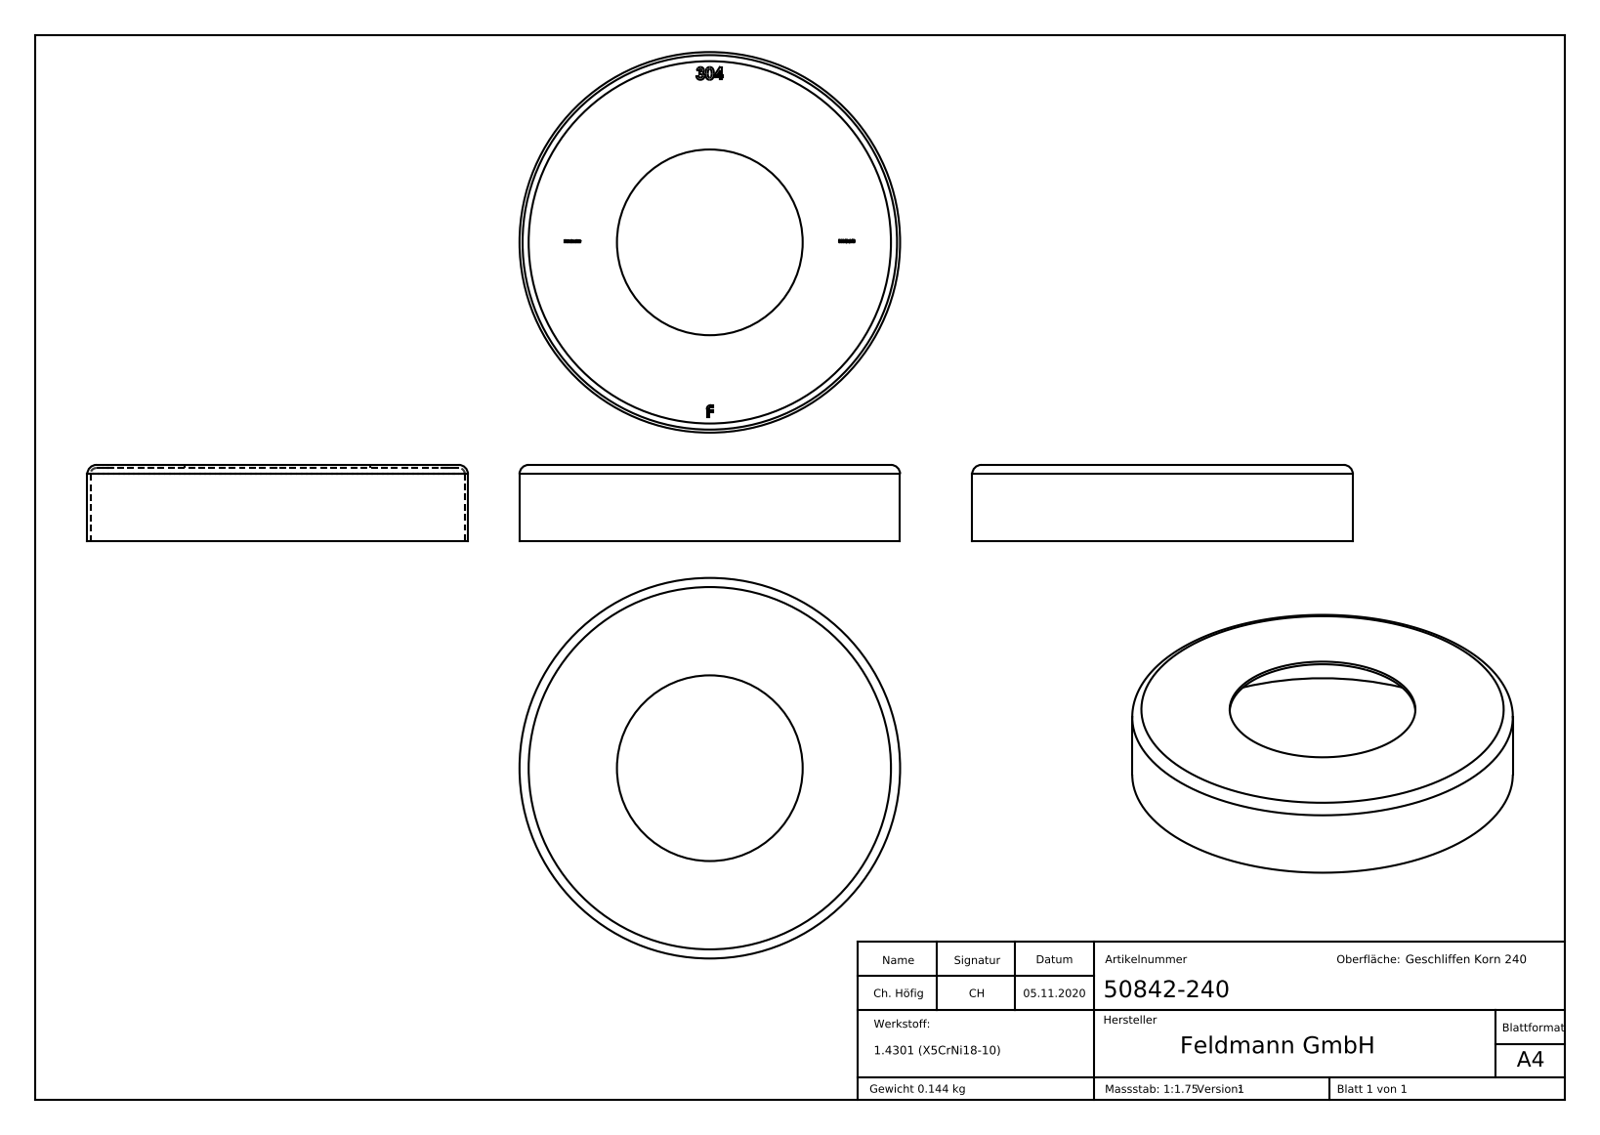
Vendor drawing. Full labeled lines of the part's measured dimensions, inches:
Part name (STEP PRODUCT): 50842-240
STEP written by: SolidWorks 2018 (CONFIG_CONTROL_DESIGN)
Units: inches
Bodies: 1 solid, 302 faces (164 planar, 6 cylindrical, 132 other)
Overall size (bounding box): 4.921 × 4.921 × 0.984
Volume: 1.115 in³ · Surface area: 57.58 in²
Round holes (diameter × count): ⌀2.402 ×1, ⌀4.843 ×1
Round bosses / shafts (diameter × count): ⌀4.921 ×1
Main face-to-face distances: 0.039, 0.945, 0.984, 0.949, 0.035, 0.028, 0.197, 0.169, 0.023, 0.027
